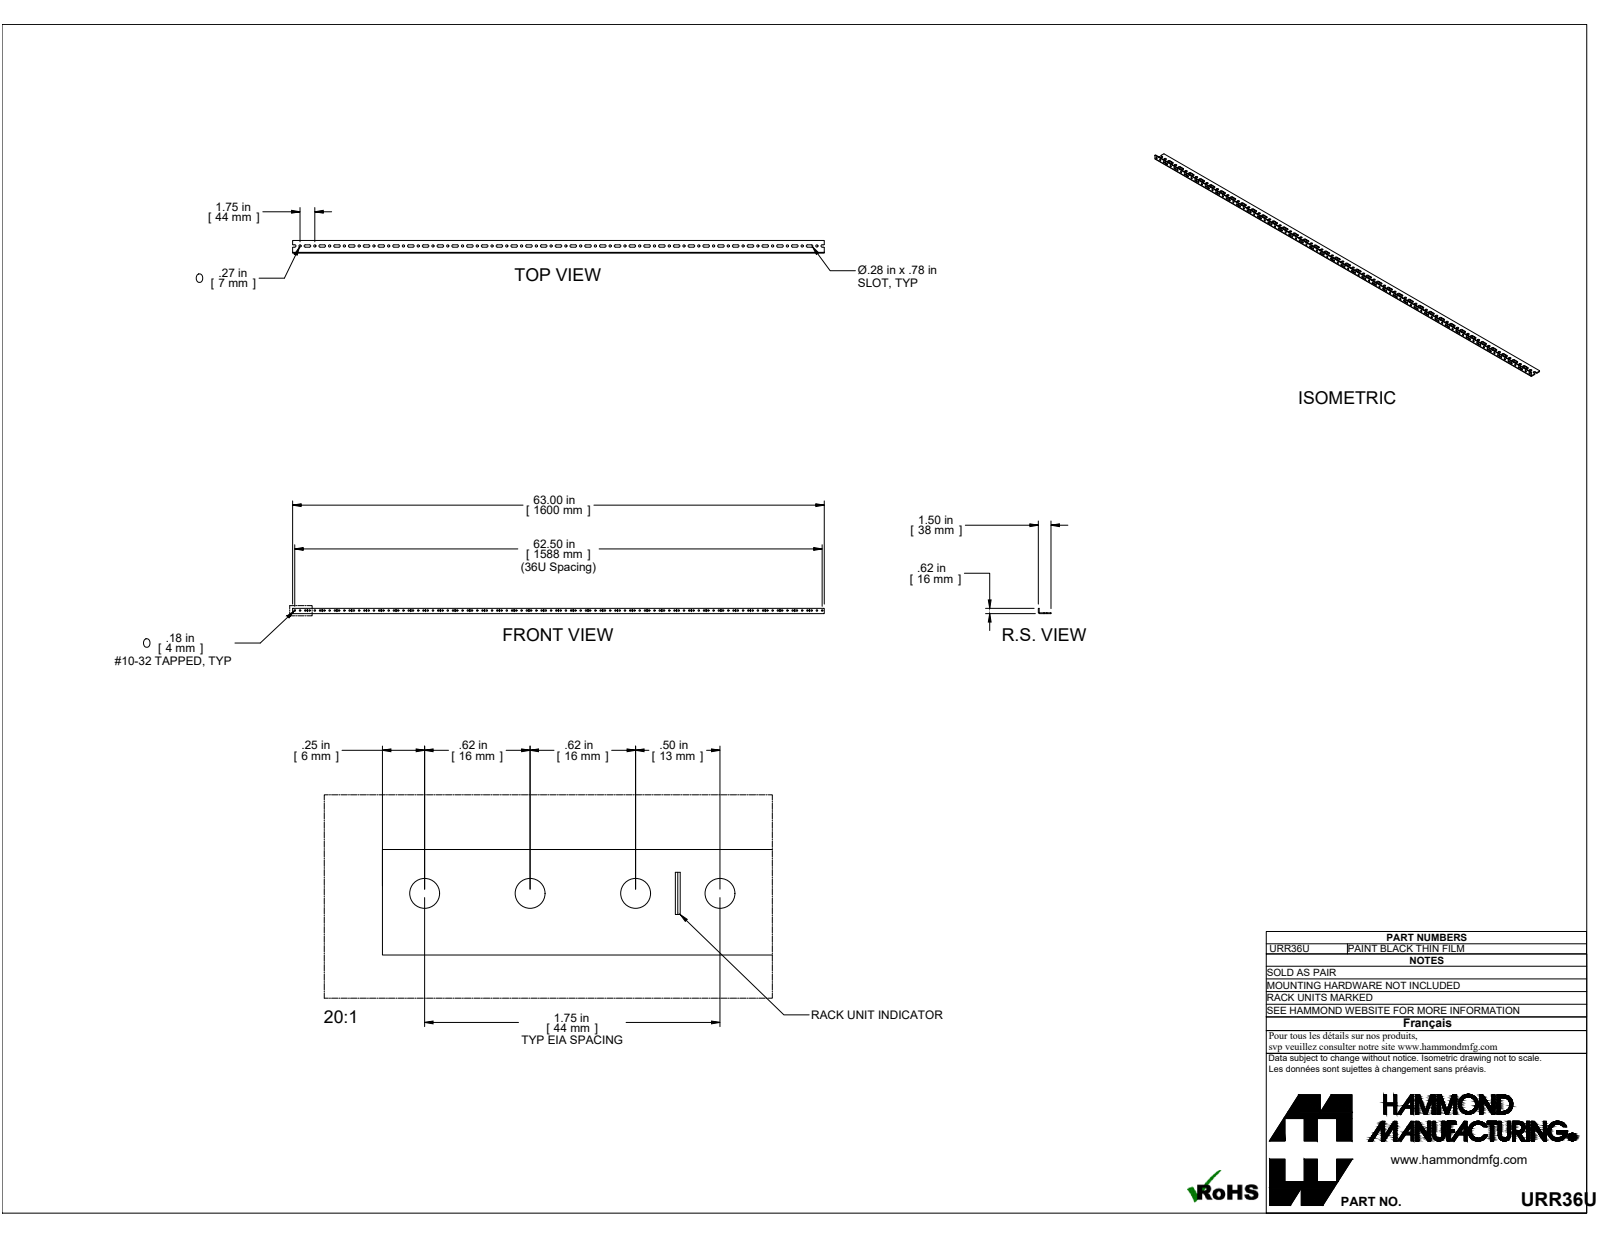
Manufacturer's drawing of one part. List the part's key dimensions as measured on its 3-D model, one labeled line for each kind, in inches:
Part name (STEP PRODUCT): COM57213-36
STEP written by: ST-DEVELOPER v16.7 (AUTOMOTIVE_DESIGN)
Units: inches
Bodies: 1 solid, 448 faces (230 planar, 218 cylindrical, 0 other)
Overall size (bounding box): 63 × 1.5 × 0.625
Volume: 10.77 in³ · Surface area: 254.3 in²
Round holes (diameter × count): ⌀0.177 ×108, ⌀0.266 ×36
Partial cylindrical surfaces — rounded edges, fillets, slot ends (radius × count): R0.141 ×72, R0.048 ×1, R0.143 ×1
Main face-to-face distances: 0.095, 0.625, 0.53, 1.5, 1.405, 0.702, 0.983, 0.607, 0.889, 0.281
Hole centre spacings: 3.5, 1.75, 5.25, 7, 10.5, 8.75, 12.25, 1.75
